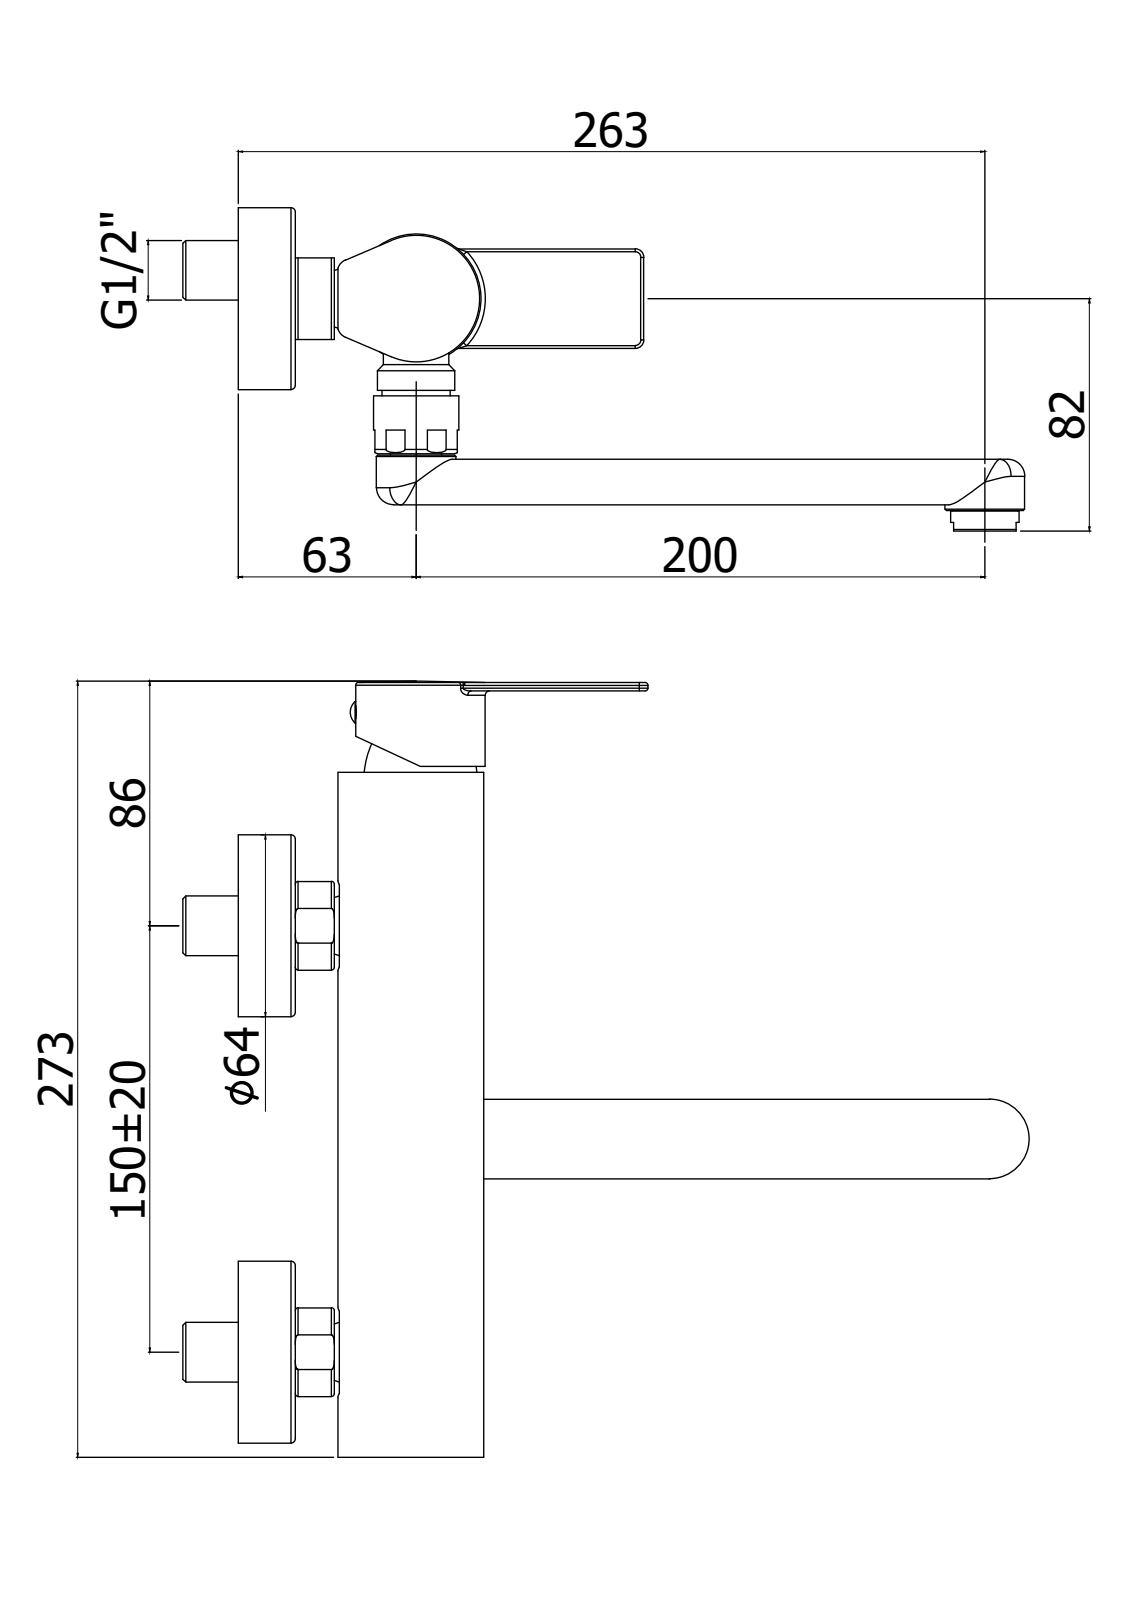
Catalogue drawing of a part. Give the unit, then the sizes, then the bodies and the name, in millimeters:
Units: millimetres
Overall size (bounding box): 277 × 273.1 × 114.2
Round bosses / shafts (diameter × count): ⌀63.5 ×2, ⌀28 ×2, ⌀24 ×2, ⌀45.5 ×1, ⌀30 ×1, ⌀27.2 ×1, ⌀23 ×1, ⌀7.6 ×1
Partial cylindrical surfaces — rounded edges, fillets, slot ends (radius × count): R1 ×6, R1.5 ×2, R3 ×2, R5 ×2, R8 ×2, R15.6 ×2, R18.5 ×2, R23.25 ×1
Main face-to-face distances: 20, 35, 15, 16, 3, 241, 272.6, 31.6, 269.6, 28.6
Bodies: 0 solids, 146 faces (49 planar, 45 cylindrical, 52 other)
Part name (STEP PRODUCT): TA161CR
STEP written by: CREO PARAMETRIC BY PTC INC, 2020044 (CONFIG_CONTROL_DESIGN)
